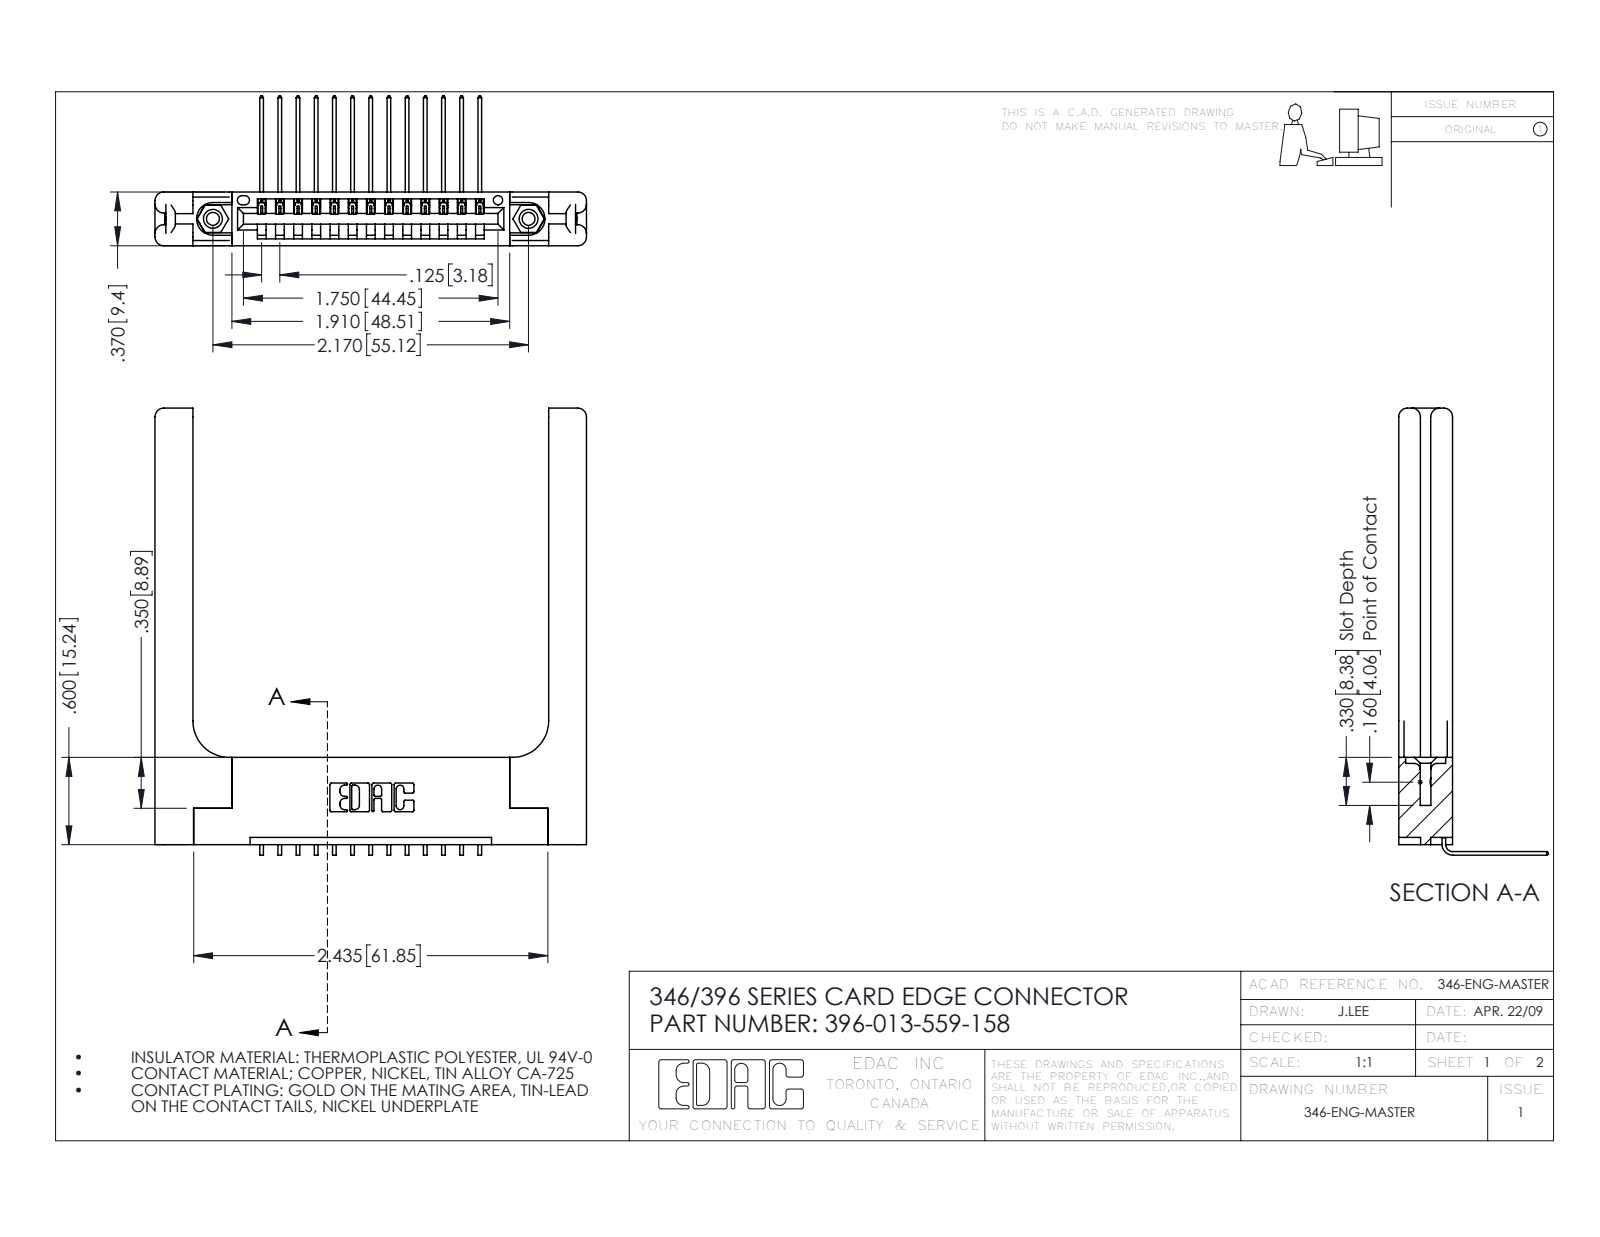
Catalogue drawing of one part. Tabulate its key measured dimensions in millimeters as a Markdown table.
| quantity | value |
| --- | --- |
| part name | 345-250-001_345-250-001-102; 346 Part_Flush Mounting Lugs - 0.156 Dia-TH; 345-292-001_558 559 Tail - 1; 346-220-058_345-220-058 (+1 more) |
| STEP written by | SolidWorks 2016 (CONFIG_CONTROL_DESIGN) |
| units | millimeters |
| bodies | 18 solids, 1158 faces (770 planar, 328 cylindrical, 60 other) |
| overall size | 78.1 × 75.3 × 26.2 |
| volume | 14 600 mm³ |
| surface area | 13 940 mm² |
| round holes (diameter × count) | 2.3 × 2, 3.2 × 2, 4 × 2, 1.6 × 1 |
| round bosses / shafts (diameter × count) | 3.9 × 2 |
| partial cylindrical surfaces (radius × count) | 0.2 × 26, 0.3 × 22, 1.5 × 16, 0.2 × 6, 0.8 × 6, 0.7 × 3, 0.8 × 2, 0.8 × 2 |
| main face-to-face distances | 9.4, 3.8, 1.8, 8.2, 1.2, 3.8, 5.6, 6.4, 2.6, 4.4 |
| hole center spacings | 6.2, 49.9, 55.1 |
